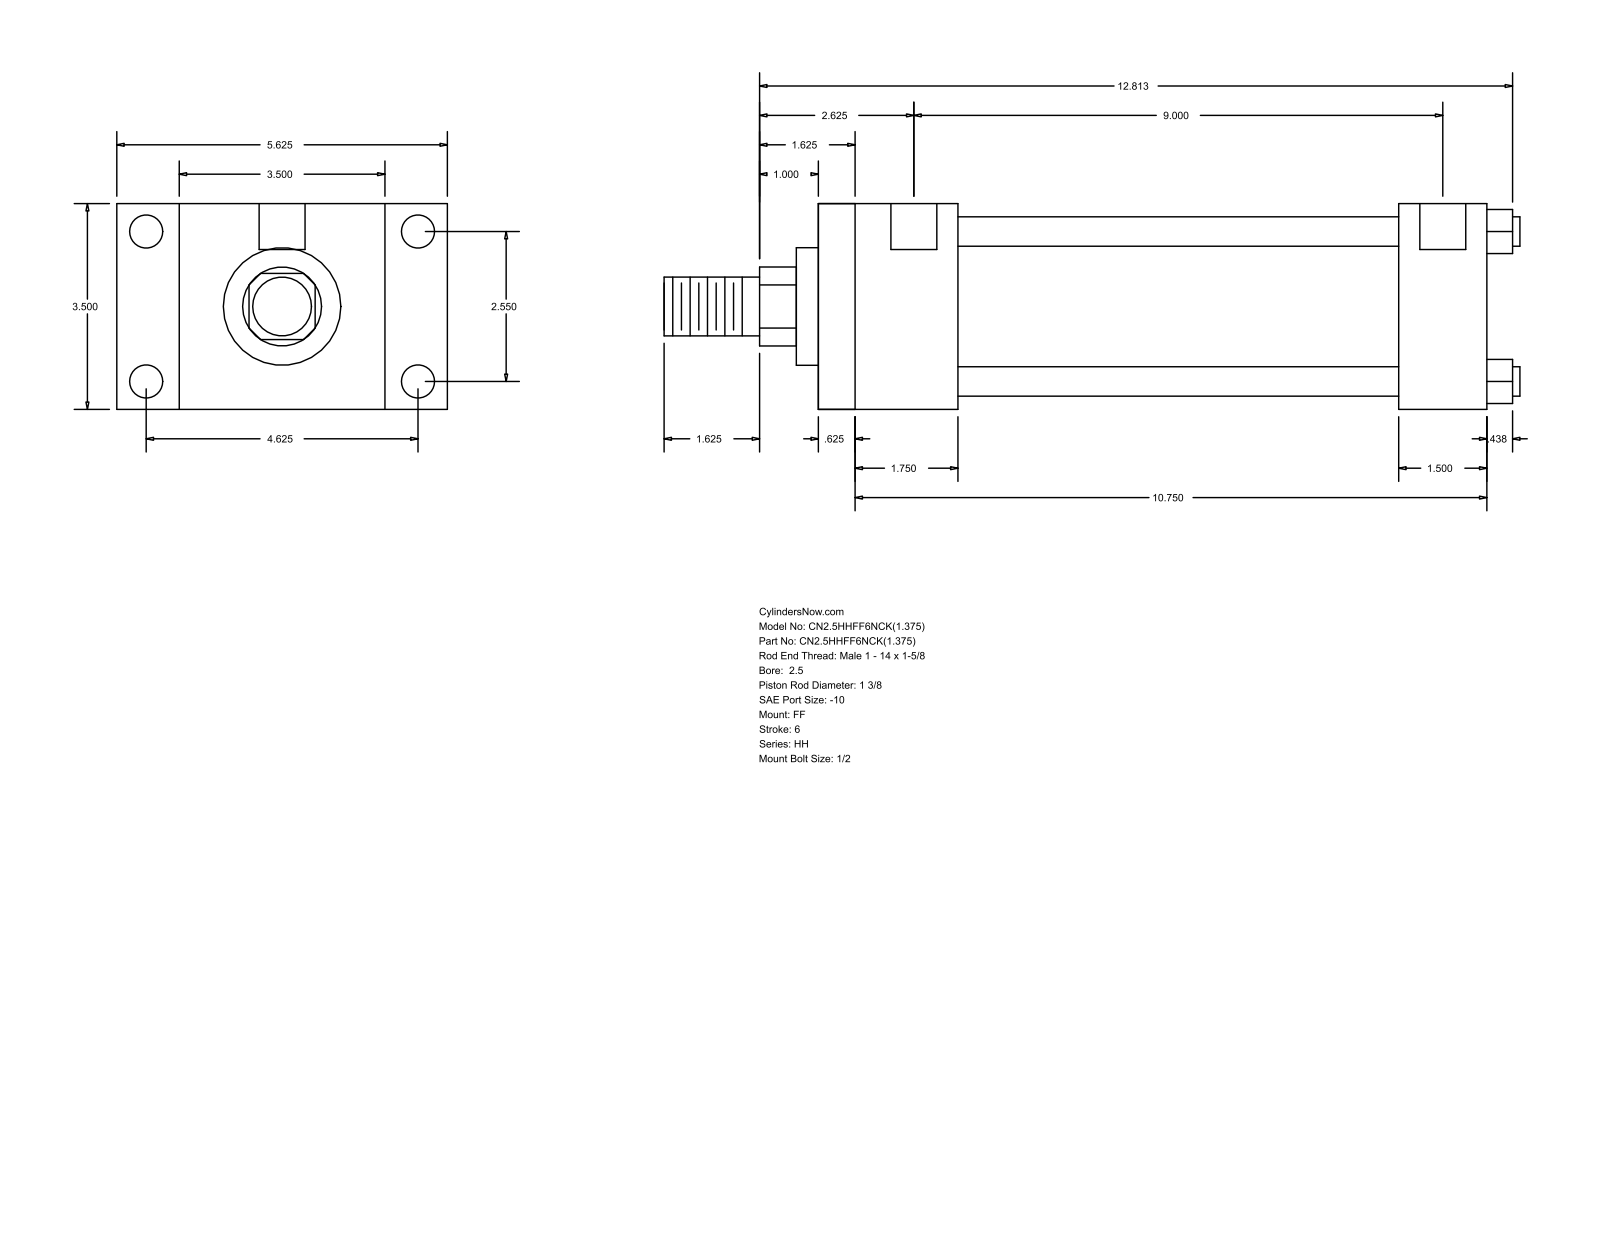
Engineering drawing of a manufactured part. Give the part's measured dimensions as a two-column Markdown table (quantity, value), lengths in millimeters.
| quantity | value |
| --- | --- |
| part name | HH_FF__0250_1.375 |
| STEP written by | GSSL Pune (CONFIG_CONTROL_DESIGN) |
| units | millimeters |
| bodies | 0 solids, 92 faces (64 planar, 28 cylindrical, 0 other) |
| overall size | 369.89 × 142.88 × 88.9 |
| round holes (diameter × count) | 5.56 × 4, 14.3 × 4, 19.84 × 2 |
| round bosses / shafts (diameter × count) | 12.7 × 4, 73.03 × 1, 50.8 × 1, 34.92 × 1, 25.4 × 1 |
| partial cylindrical surfaces (radius × count) | 17.06 × 1 |
| main face-to-face distances | 88.9, 288.92, 15.87, 273.05, 60.32, 44.45, 228.6, 250.83, 234.96, 190.51 |
| hole center spacings | 64.76, 117.48, 134.15, 231.77, 1.58, 1.59, 228.6, 230.18 |
